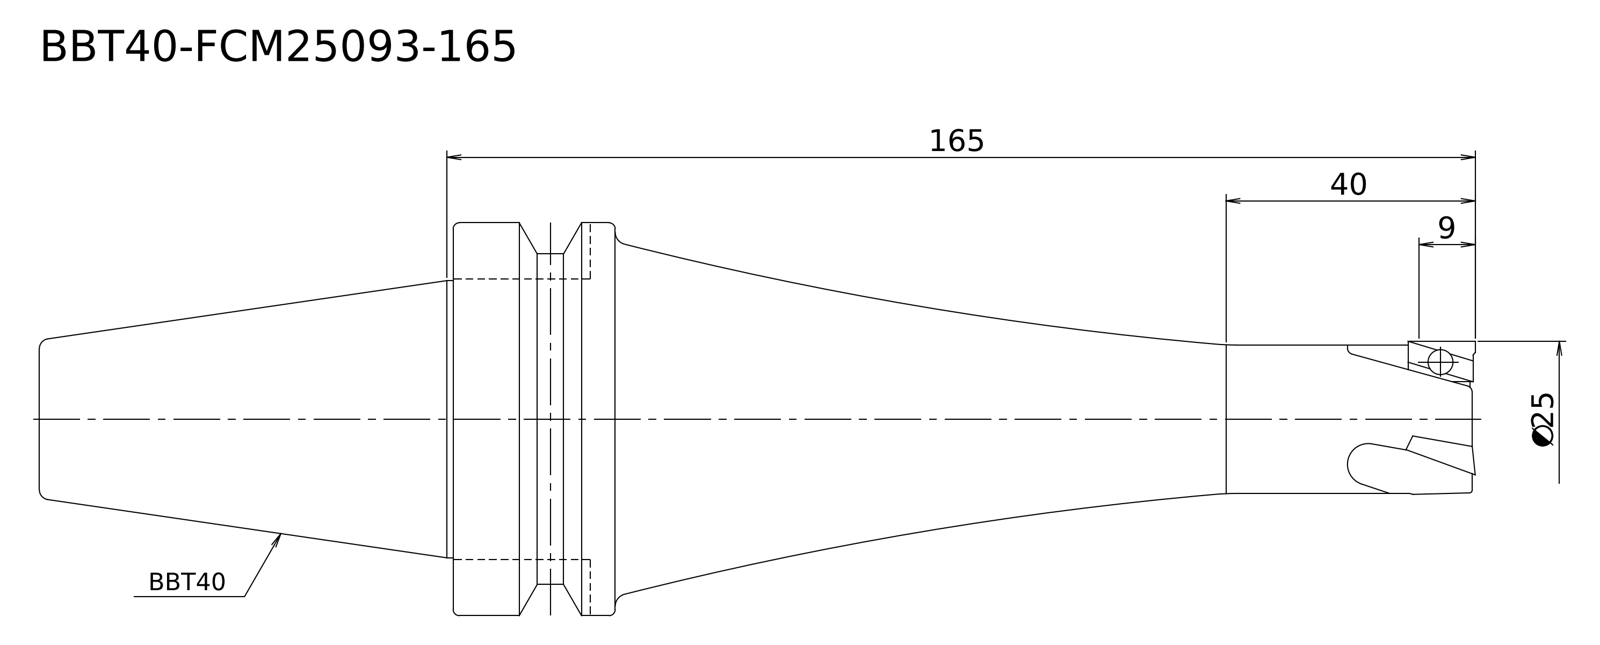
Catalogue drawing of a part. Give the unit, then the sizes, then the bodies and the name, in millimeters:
Units: millimetres
Overall size (bounding box): 230.4 × 63 × 63
Round bosses / shafts (diameter × count): ⌀63 ×1, ⌀53 ×1, ⌀44.45 ×1, ⌀25 ×1, ⌀23.8 ×1
Main face-to-face distances: 66.4, 164, 230.4, 138, 26, 92.4
Volume: 289 304 mm³ · Surface area: 31 939 mm²
Bodies: 1 solid, 16 faces (4 planar, 6 cylindrical, 6 other)
STEP written by: Kubotek KeyCreator V8.5.1 (14335) (CONFIG_CONTROL_DESIGN)
